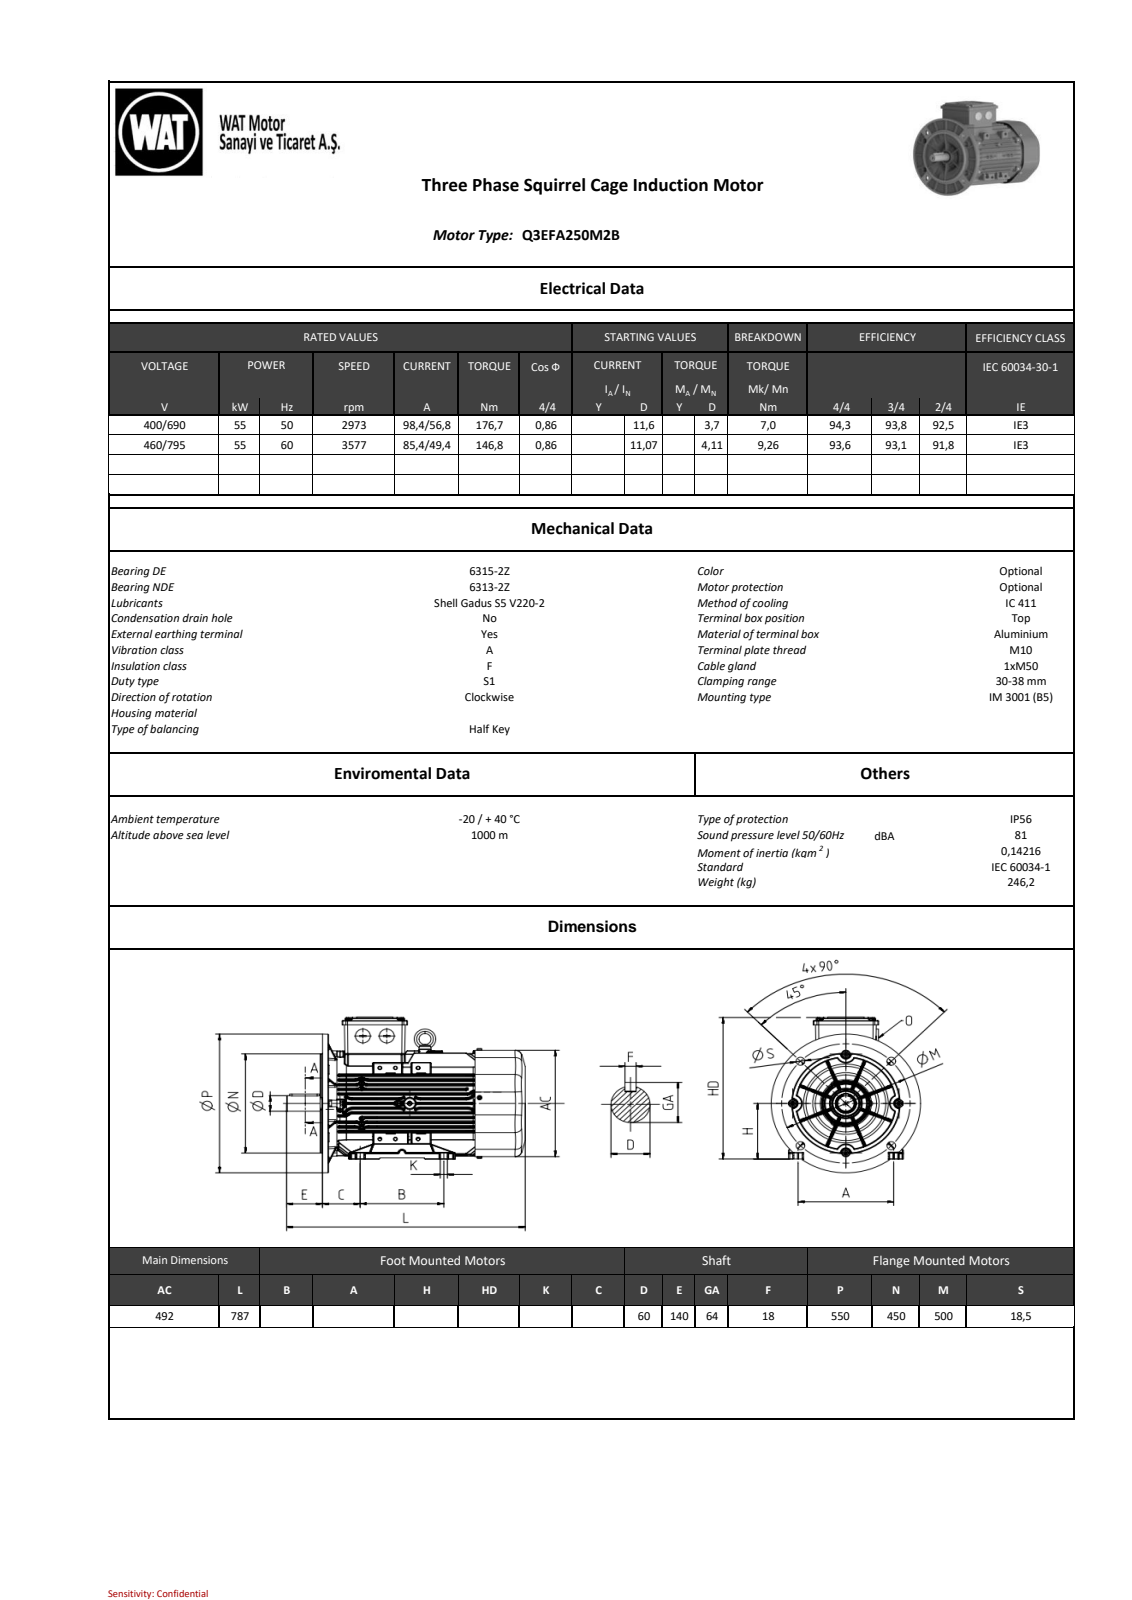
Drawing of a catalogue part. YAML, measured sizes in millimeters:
part_name: "001_objects"
step_written_by: "SIEMENS PLM Software NX2206.8101 (AUTOMOTIVE_DESIGN)"
units: millimeters
bodies: {solids: 0, faces: 14429, planar: 6514, cylindrical: 3812, other: 4103}
overall_size: [787, 557.5, 550]
round_holes:
  - {diameter: 8.5, count: 9}
  - {diameter: 6, count: 8}
  - {diameter: 9.15, count: 8}
  - {diameter: 19, count: 8}
  - {diameter: 10.2, count: 7}
  - {diameter: 0.7, count: 6}
  - {diameter: 5, count: 5}
  - {diameter: 7.5, count: 5}
  - {diameter: 11, count: 5}
  - {diameter: 18.5, count: 5}
  - {diameter: 4.3, count: 4}
  - {diameter: 5.5, count: 4}
round_bosses_or_shafts:
  - {diameter: 10, count: 14}
  - {diameter: 15.73, count: 8}
  - {diameter: 18.1, count: 7}
  - {diameter: 14.8, count: 4}
  - {diameter: 12.73, count: 4}
  - {diameter: 8, count: 4}
  - {diameter: 5, count: 4}
  - {diameter: 5.85, count: 3}
partial_cylinders:
  - {radius: 1, count: 966}
  - {radius: 0.2, count: 332}
  - {radius: 2, count: 328}
  - {radius: 0.5, count: 271}
  - {radius: 5, count: 237}
  - {radius: 2.5, count: 150}
  - {radius: 4, count: 87}
  - {radius: 1.01, count: 49}
face_to_face_distances: [9, 189.81, 15.53, 169.04, 20.77, 14.83, 5, 184.57, 5.24, 3]
hole_center_spacings: [7.4, 156, 146.34, 45.26, 68.18, 98.65, 186.17, 192.6]
